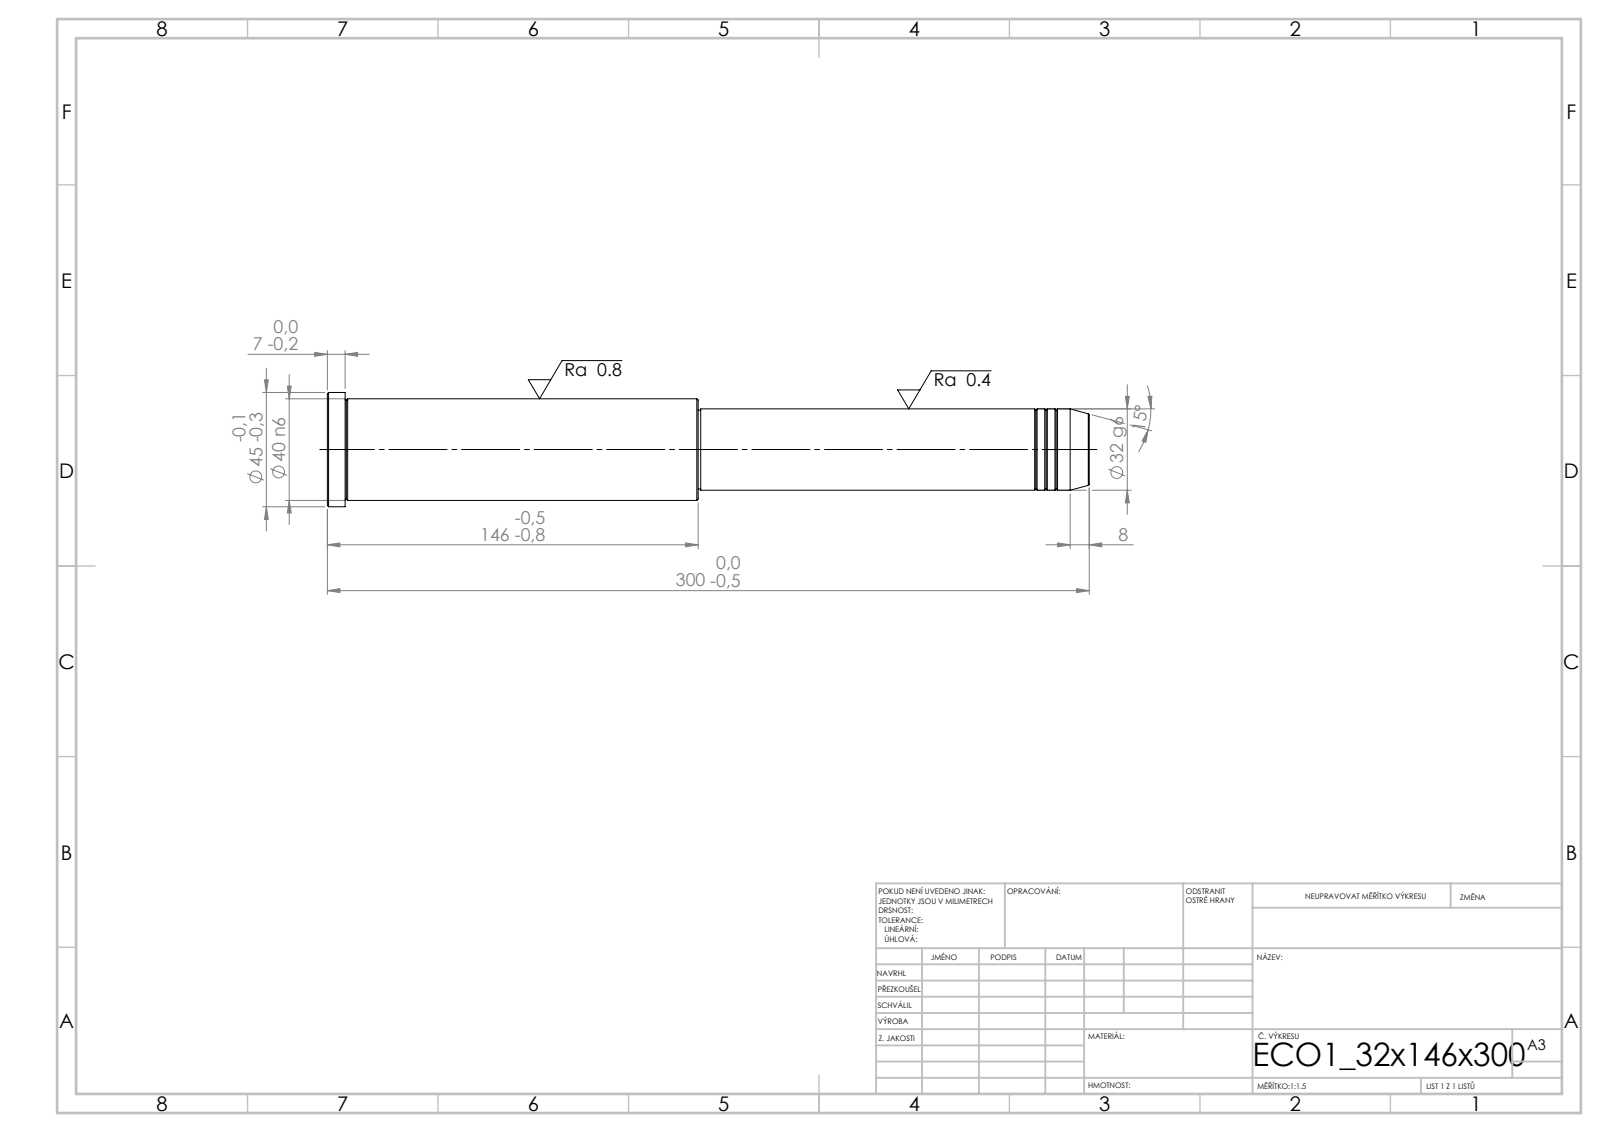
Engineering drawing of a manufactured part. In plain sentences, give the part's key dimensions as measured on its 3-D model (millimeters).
Its 3-D file was written by "SolidWorks 2019 (CONFIG_CONTROL_DESIGN)". It is 1 solid with 43 faces: 5 planar, 14 cylindrical and 24 other. Overall it measures 300 by 45 by 45 millimeters. Its volume is 308 683 cubic millimeters and its surface area 37 146 square millimeters. Round bosses or shafts: 1 of diameter 45, 1 of diameter 40, 1 of diameter 32, 1 of diameter 31. The main face-to-face distances are 300, 154, 146, 293, 139, 7, 153, 1, 140, 147.
